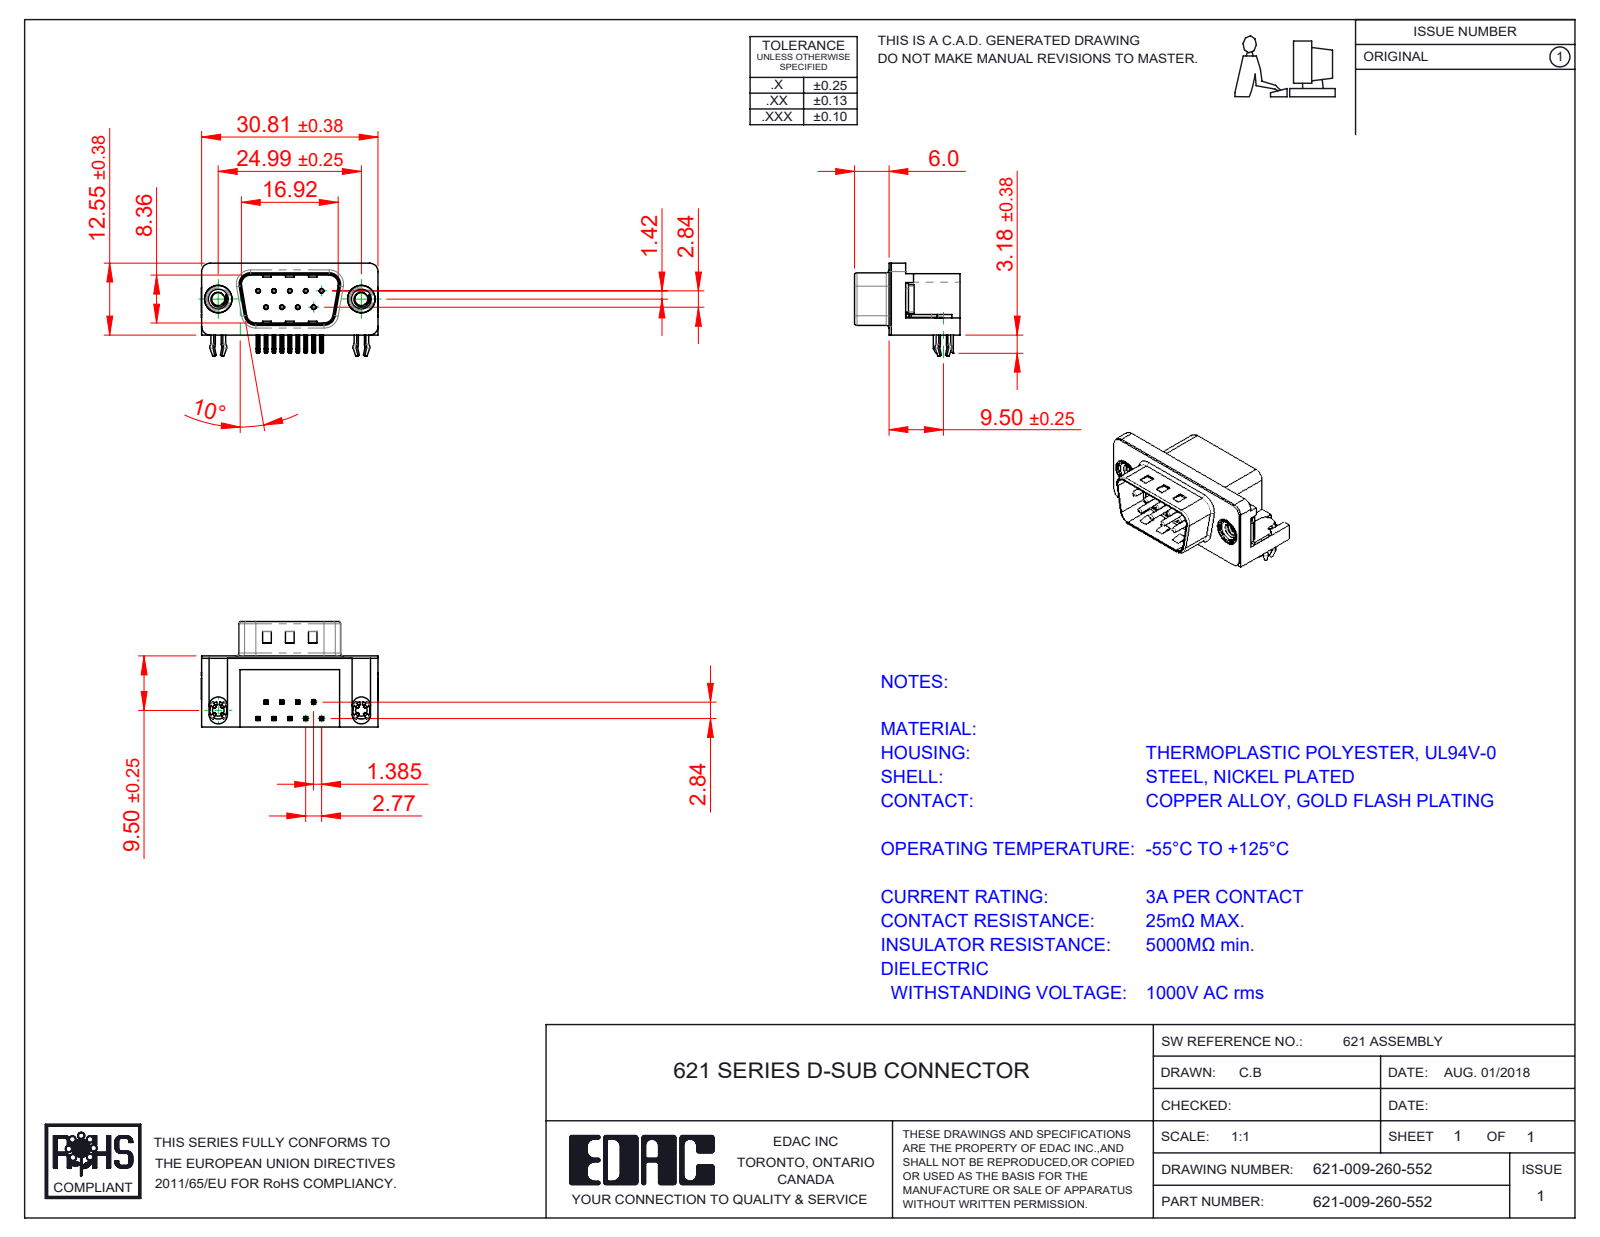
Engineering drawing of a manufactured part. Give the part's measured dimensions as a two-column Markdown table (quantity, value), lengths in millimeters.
| quantity | value |
| --- | --- |
| part name | 621 Contact Bottom; 621 4-40 Threaded Rivet; 621-009-260-552; 621 Shell_9 Socket (+3 more) |
| STEP written by | SolidWorks 2016 (CONFIG_CONTROL_DESIGN) |
| units | millimeters |
| bodies | 15 solids, 1021 faces (573 planar, 327 cylindrical, 121 other) |
| overall size | 30.89 × 18.4 × 15.73 |
| volume | 3 259 mm³ |
| surface area | 4 500 mm² |
| round holes (diameter × count) | 0.35 × 9, 0.8 × 9, 2.26 × 4, 4 × 2, 4.8 × 2, 5 × 2 |
| round bosses / shafts (diameter × count) | 0.75 × 9, 4.9 × 2, 4.75 × 2, 3.9 × 2, 3.26 × 2 |
| partial cylindrical surfaces (radius × count) | 0.25 × 44, 0.12 × 18, 1 × 16, 0.5 × 9, 1.5 × 8, 1.6 × 8, 0.9 × 4, 2 × 4 |
| main face-to-face distances | 0.4, 12, 12.4, 10.35, 2.9, 9.5, 2.5, 0.5, 2.1, 0.35 |
| hole center spacings | 3.16, 2.77, 5.54, 5.03, 5.04, 8.31, 7.48, 7.49 |
